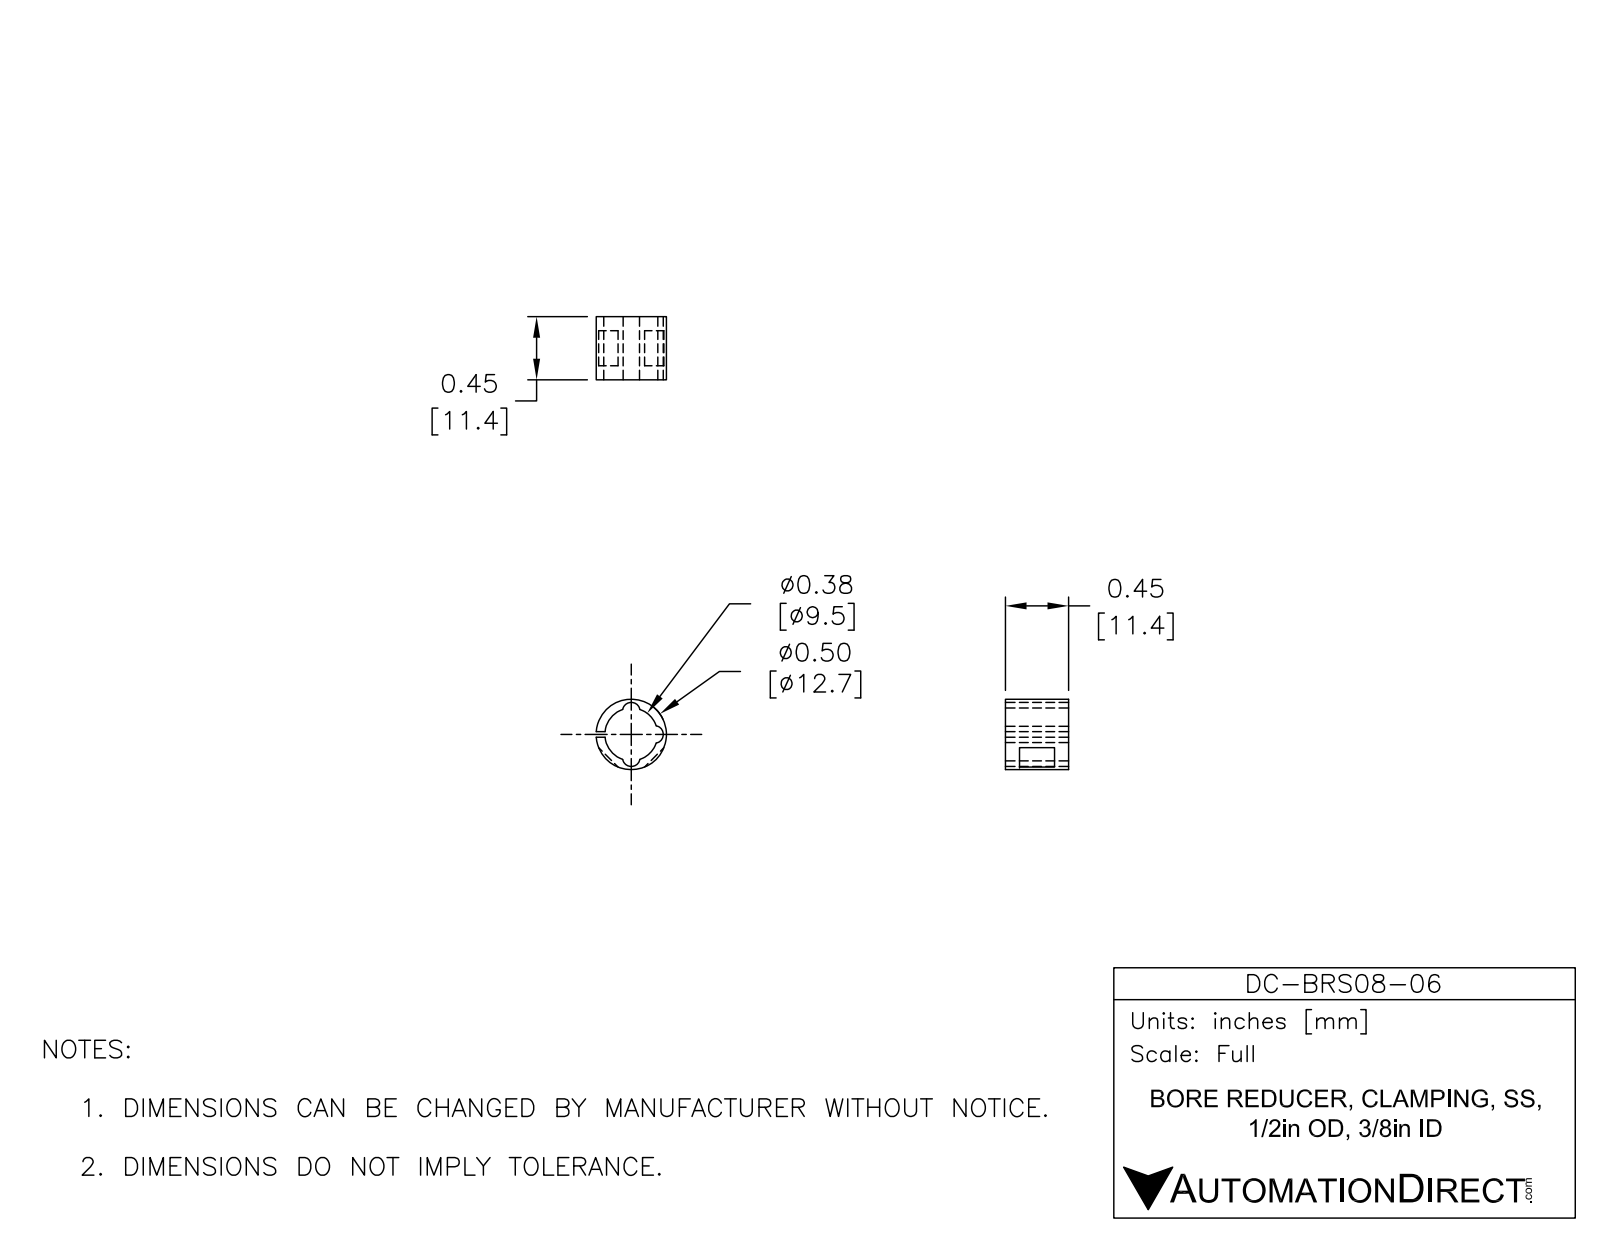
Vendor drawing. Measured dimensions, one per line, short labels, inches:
name: DC-BRS08-06
written by: SolidWorks 2015 (AUTOMOTIVE_DESIGN)
unit: in
bodies: 1 solid, 21 faces (10 planar, 11 cylindrical, 0 other)
size: 0.5 × 0.499 × 0.449
volume: 0.031 in³; area: 1.47 in²
bosses: 1× ⌀0.5
rounds: 3× R0.063, 1× R0.187
face distances: 0.449, 0.04, 0.1, 0.349, 0.249
